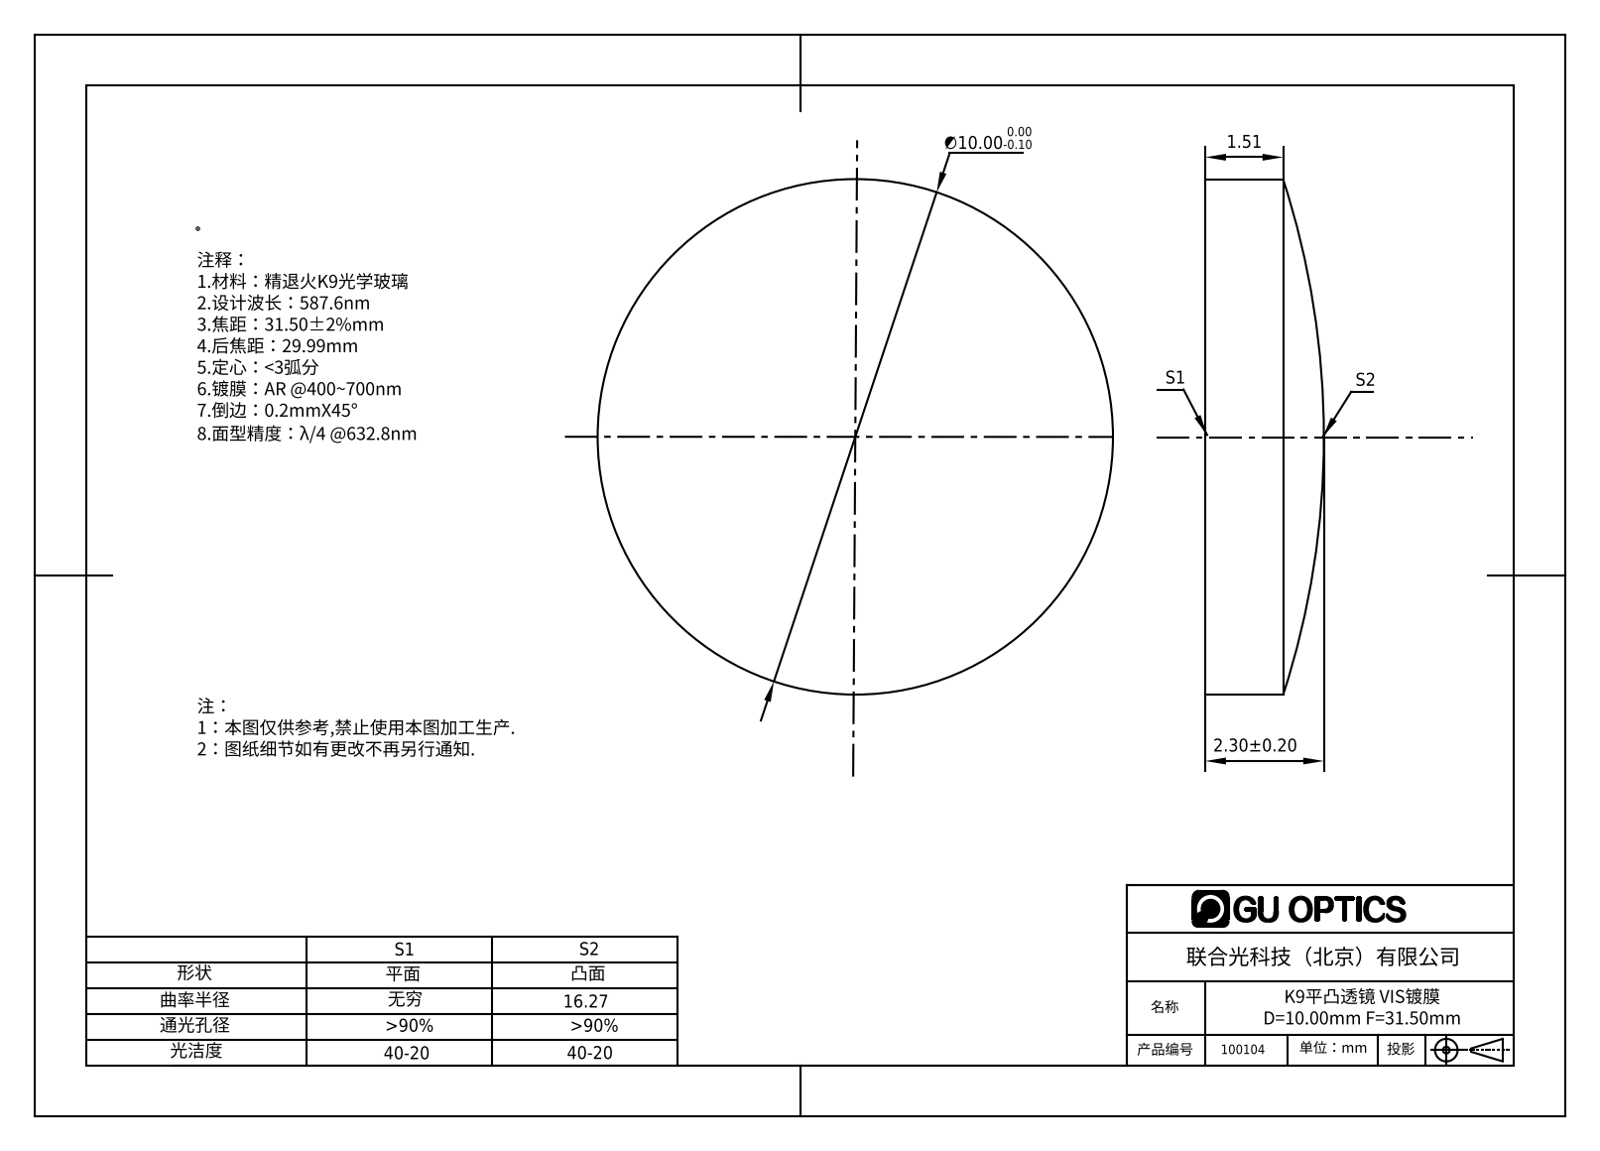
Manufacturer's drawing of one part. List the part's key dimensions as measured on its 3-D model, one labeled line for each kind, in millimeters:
Part name (STEP PRODUCT): 100104
STEP written by: SolidWorks 2016 (AUTOMOTIVE_DESIGN)
Units: millimetres
Bodies: 1 solid, 5 faces (1 planar, 2 cylindrical, 2 other)
Overall size (bounding box): 10 × 10 × 2.3
Volume: 150 mm³ · Surface area: 206 mm²
Round bosses / shafts (diameter × count): ⌀10 ×1
